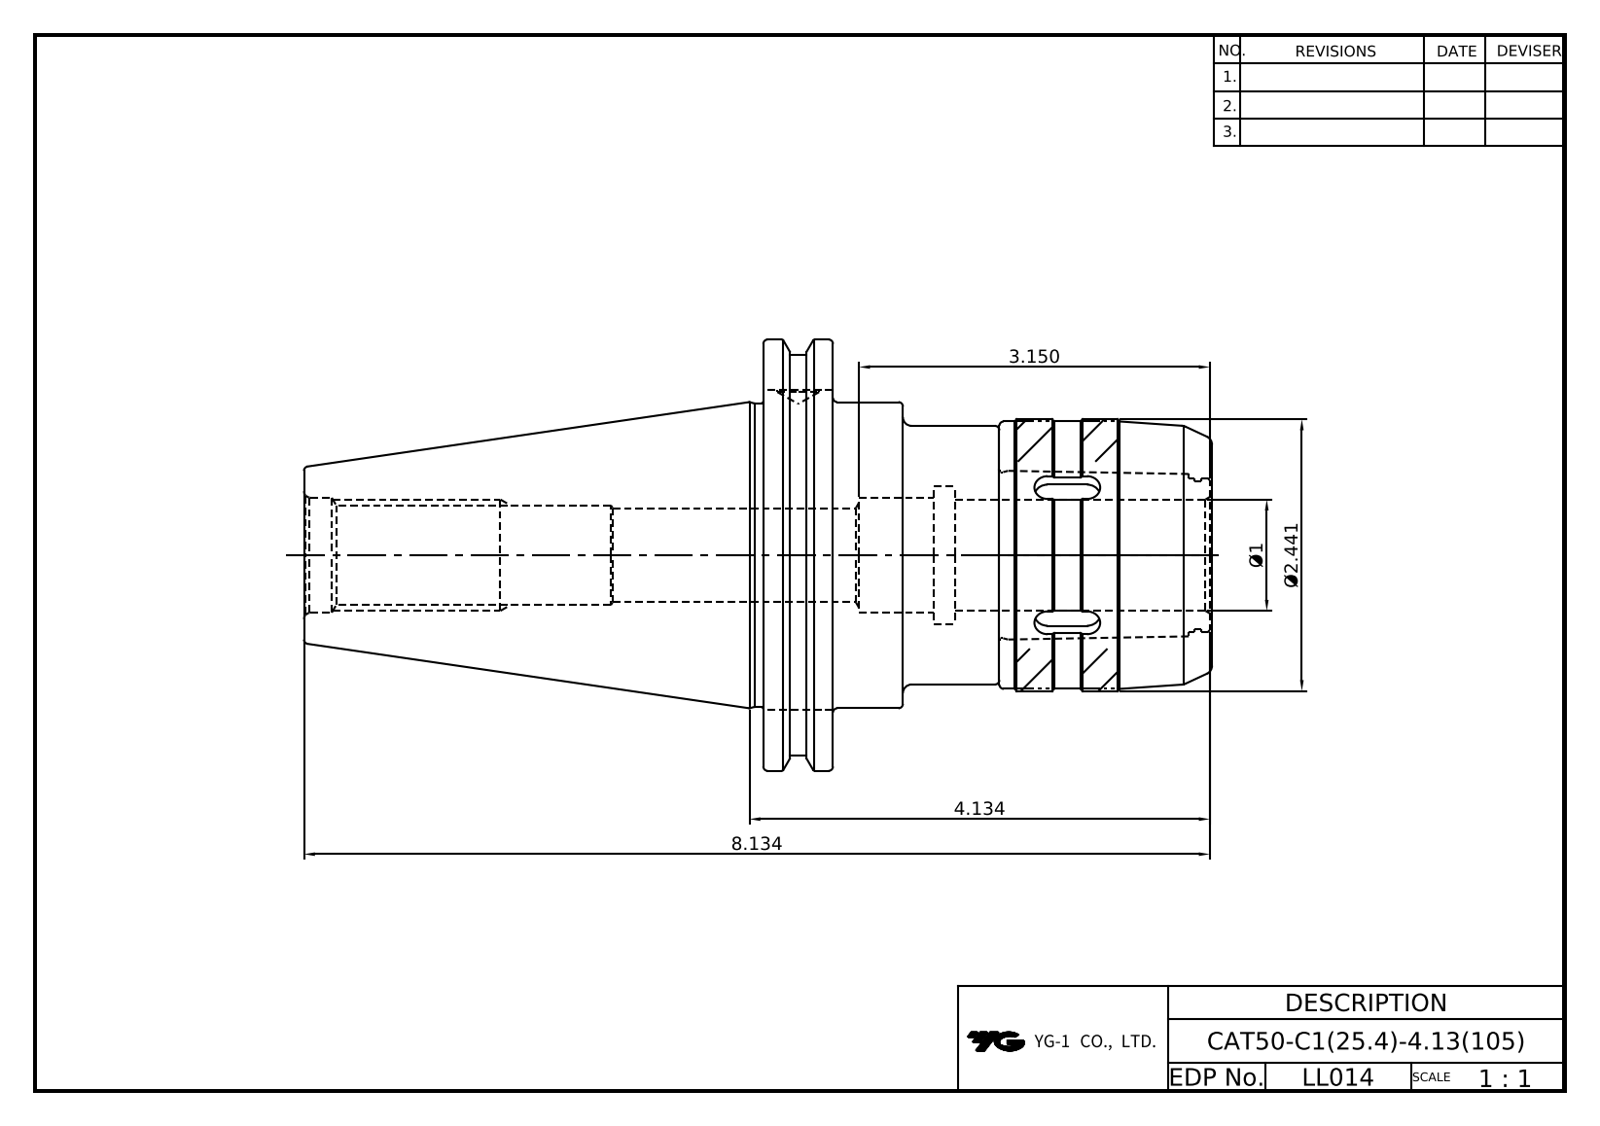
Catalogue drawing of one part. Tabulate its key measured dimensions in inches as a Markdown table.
| quantity | value |
| --- | --- |
| part name | CAT50-C25.4-105; C25-CAP |
| STEP written by | Autodesk Inventor 2020 (AUTOMOTIVE_DESIGN) |
| units | inches |
| bodies | 2 solids, 183 faces (82 planar, 43 cylindrical, 58 other) |
| overall size | 8.154 × 3.875 × 3.728 |
| volume | 31.73 in³ |
| surface area | 129 in² |
| round holes (diameter × count) | 0.375 × 1, 0.846 × 1, 0.865 × 1, 1 × 1, 1.024 × 1, 1.031 × 1, 1.244 × 1, 1.752 × 1, 1.829 × 1 |
| round bosses / shafts (diameter × count) | 3.875 × 1, 3.594 × 1, 2.75 × 1, 2.726 × 1, 2.441 × 1, 2.402 × 1, 2.323 × 1, 1.386 × 1 |
| partial cylindrical surfaces (radius × count) | 0.118 × 6 |
| main face-to-face distances | 0.625, 2.119, 1.494, 0.866, 4.029, 3.404, 1.909, 4.125, 4.75, 6.244 |
